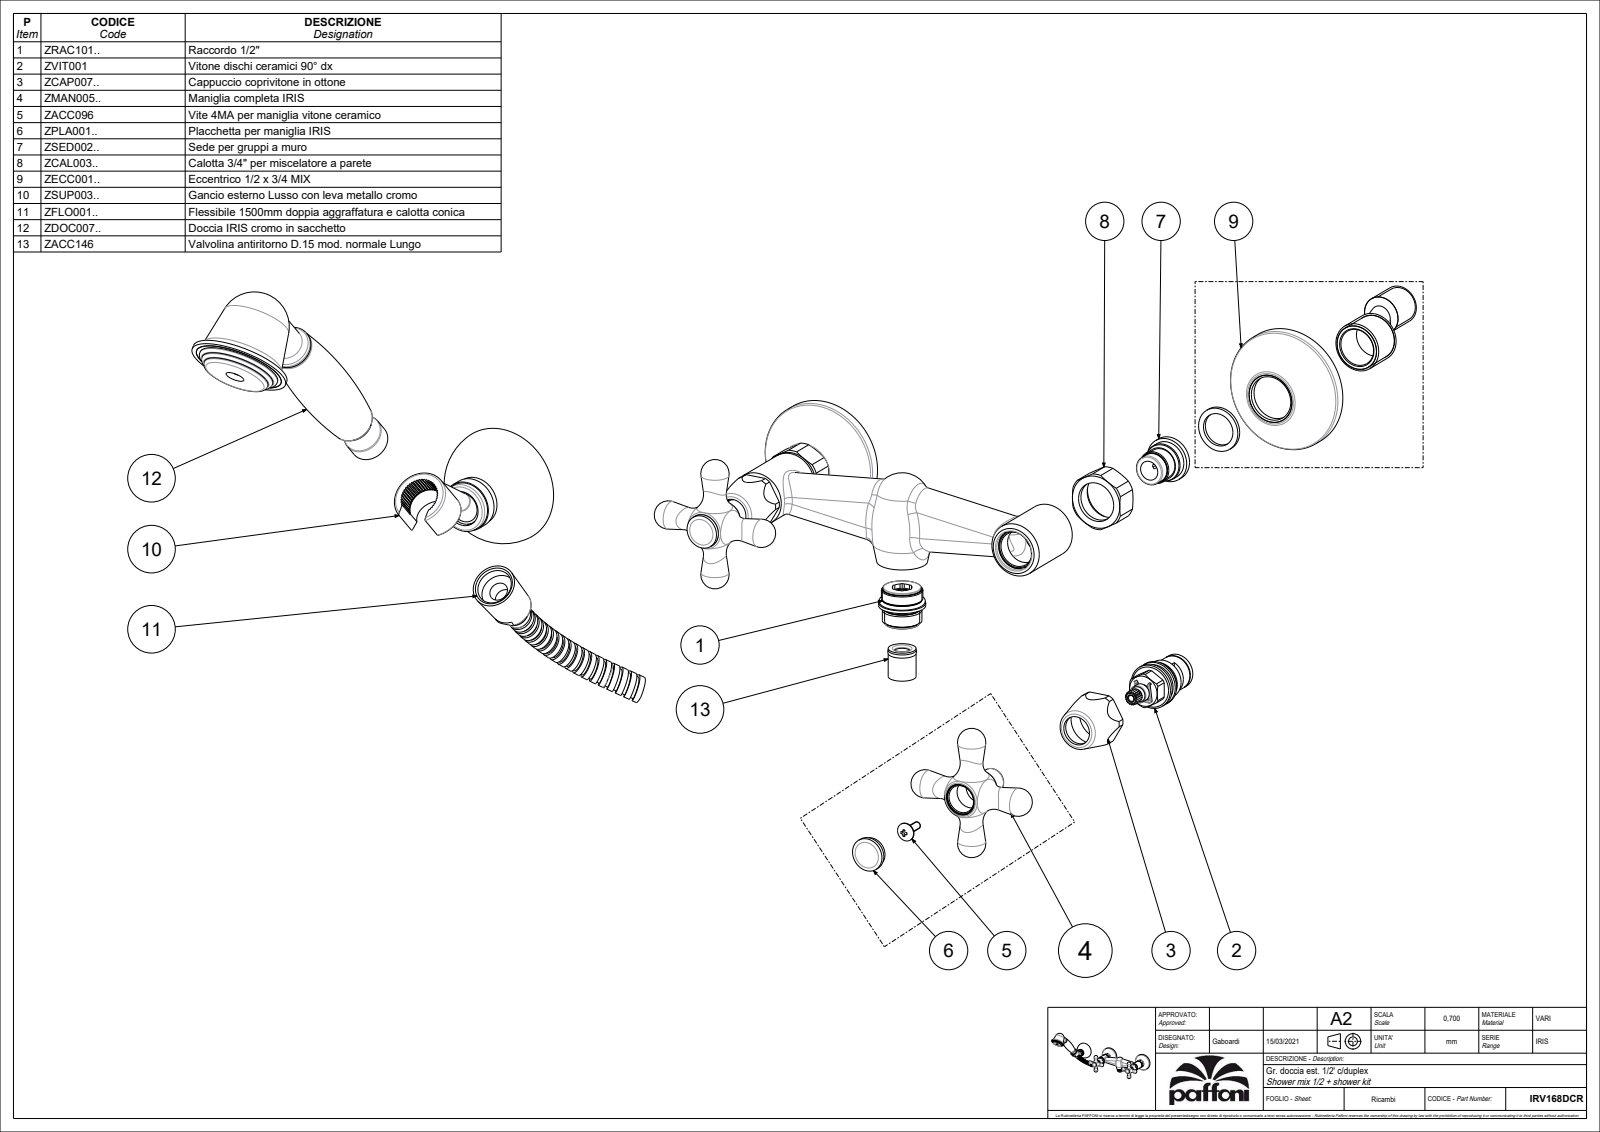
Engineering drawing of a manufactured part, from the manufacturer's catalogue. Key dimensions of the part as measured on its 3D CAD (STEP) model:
Part name (STEP PRODUCT): IRV168DCR
STEP written by: CREO PARAMETRIC BY PTC INC, 2020044 (CONFIG_CONTROL_DESIGN)
Units: millimetres
Bodies: 4 solids, 776 faces (234 planar, 148 cylindrical, 394 other)
Overall size (bounding box): 346.5 × 241.11 × 199.58
Volume: 450 166 mm³ · Surface area: 130 876 mm²
Round holes (diameter × count): ⌀8 ×2, ⌀10.5 ×2, ⌀15.7 ×2, ⌀19 ×2, ⌀21.3 ×2, ⌀22 ×2, ⌀23 ×2, ⌀14.5 ×1, ⌀15.1 ×1, ⌀21 ×1
Round bosses / shafts (diameter × count): ⌀29 ×3, ⌀18 ×3, ⌀65.5 ×2, ⌀20.5 ×2, ⌀17.7 ×2, ⌀16 ×2, ⌀13.5 ×2, ⌀53 ×1
Partial cylindrical surfaces — rounded edges, fillets, slot ends (radius × count): R10 ×5, R6.5 ×4, R12.5 ×2, R15.5 ×2, R5.25 ×1, R12 ×1
Main face-to-face distances: 16.5, 3.5, 10, 8.5, 26.5, 28.5, 12, 1.5, 34, 20
Hole centre spacings: 158
